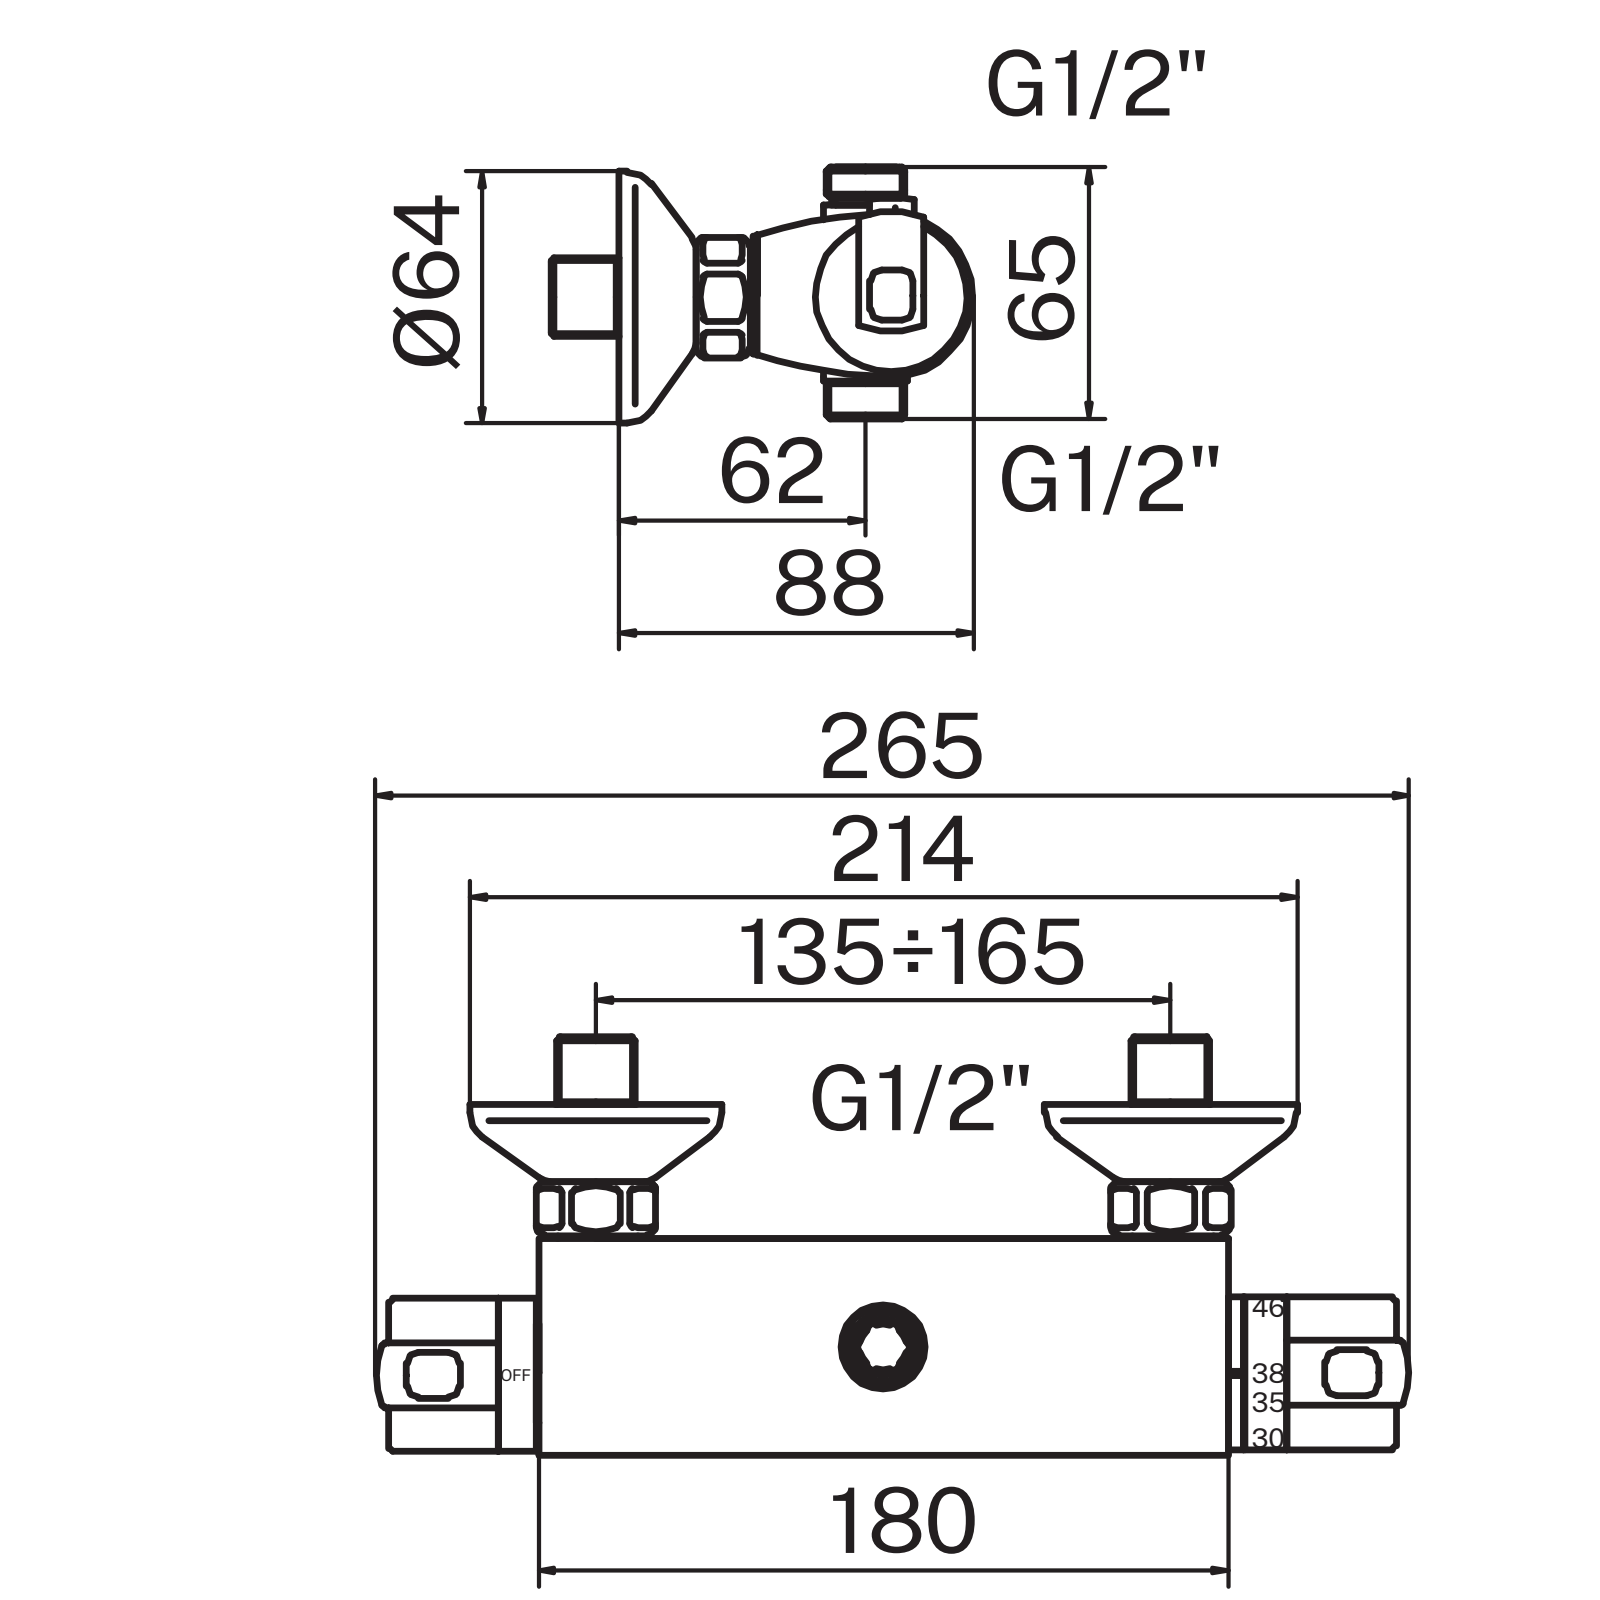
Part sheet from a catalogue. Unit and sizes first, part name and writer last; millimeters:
Units: millimetres
Overall size (bounding box): 268.4 × 104 × 65
Round holes (diameter × count): ⌀12 ×2, ⌀14 ×2, ⌀15.5 ×2, ⌀17.7 ×2, ⌀19.3 ×2, ⌀21.5 ×2, ⌀24.5 ×2, ⌀25 ×2, ⌀27 ×2, ⌀64 ×2, ⌀15 ×1, ⌀17 ×1
Round bosses / shafts (diameter × count): ⌀65 ×2, ⌀27.4 ×2, ⌀26.4 ×2, ⌀24 ×2, ⌀21 ×2, ⌀18 ×2, ⌀17 ×2, ⌀16.3 ×2
Partial cylindrical surfaces — rounded edges, fillets, slot ends (radius × count): R0.2 ×60, R0.5 ×16, R2 ×8, R1 ×5, R1.7 ×4, R1.8 ×4, R7.25 ×2, R16 ×2
Main face-to-face distances: 36.5, 221.5, 2, 260, 38.5, 223.5, 29, 217.5, 258, 40.5
Hole centre spacings: 150
Volume: 329 431 mm³ · Surface area: 118 637 mm²
Bodies: 14 solids, 730 faces (295 planar, 314 cylindrical, 121 other)
Part name (STEP PRODUCT): Importato 134; ATMA405C001; Importato 136; SSRMAC0005 (+8 more)
STEP written by: Shapr3D (AUTOMOTIVE_DESIGN)
